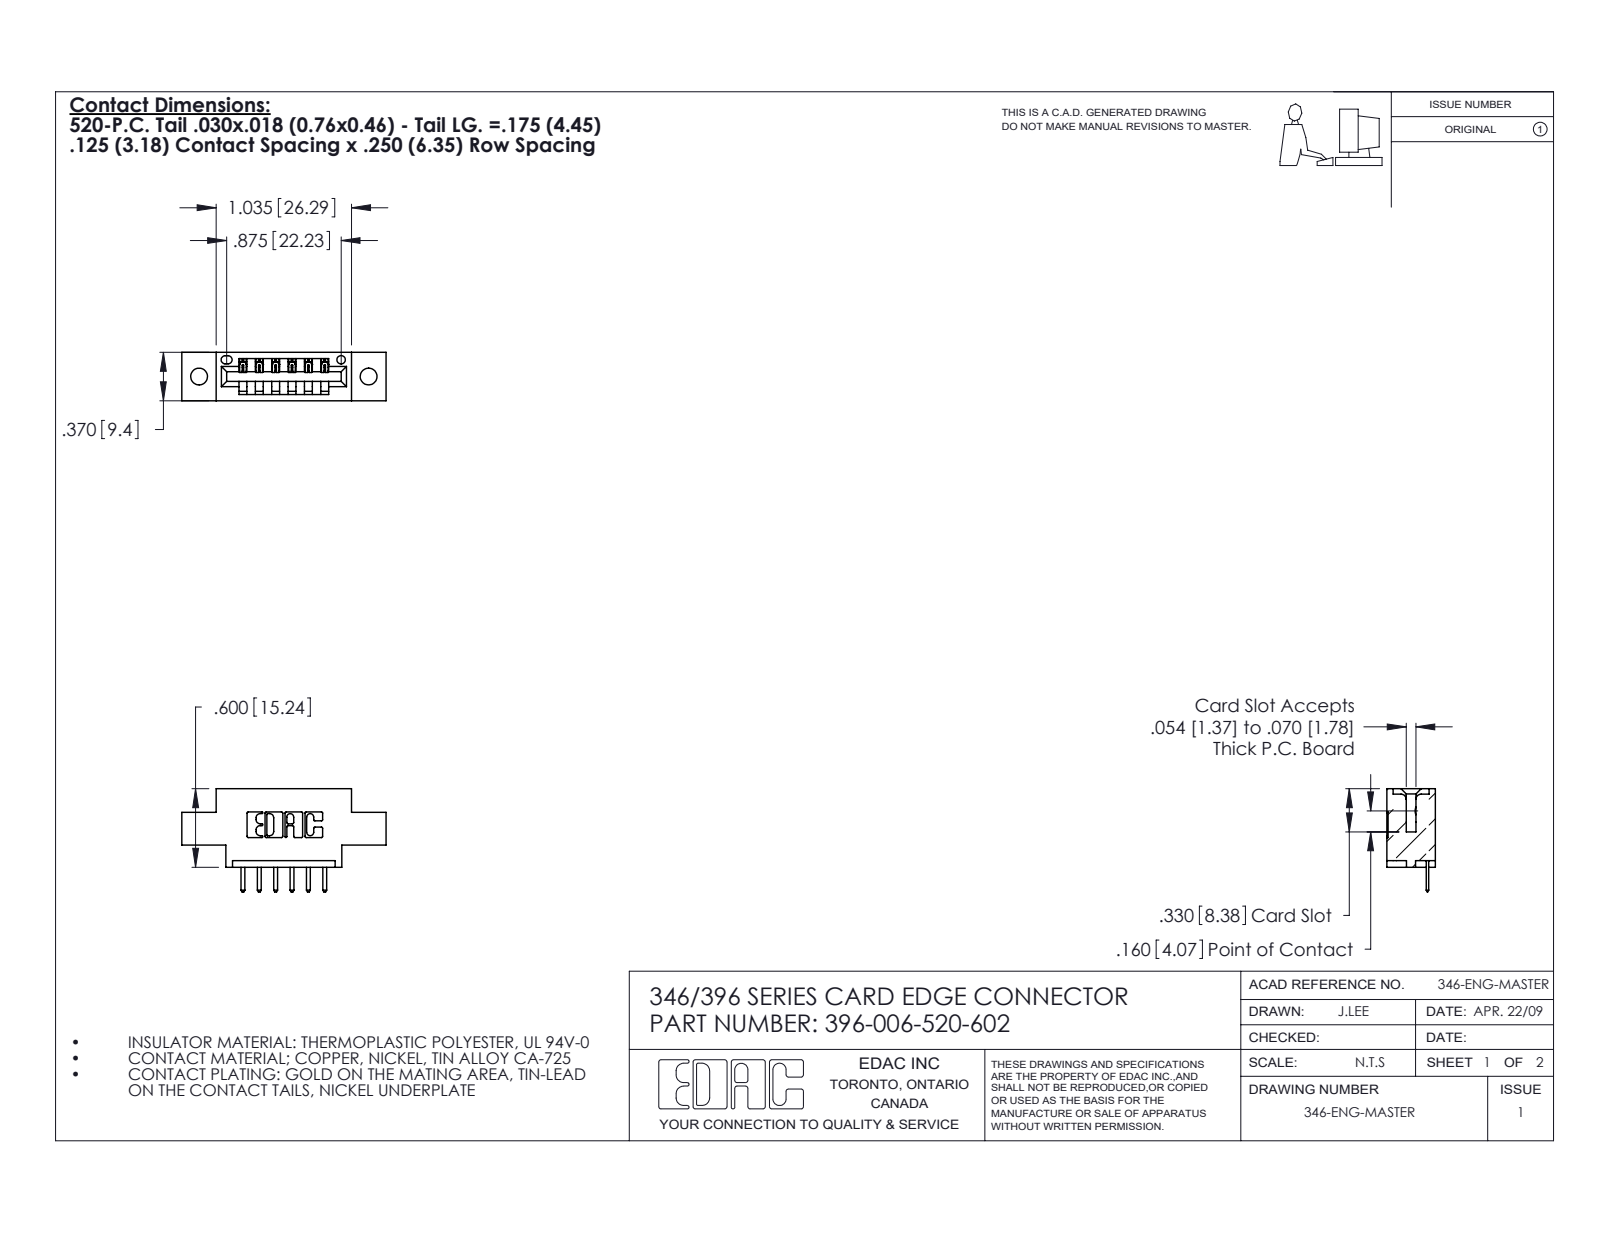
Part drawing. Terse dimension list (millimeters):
name: 345-292-001_345-293-120; 346 Part_0.170 Offset - 0.128 Dia; 396-006-520-602
written by: SolidWorks 2020 (CONFIG_CONTROL_DESIGN)
unit: mm
bodies: 7 solids, 498 faces (332 planar, 166 cylindrical, 0 other)
size: 39.6 × 20 × 9.4
volume: 3 340 mm³; area: 3 613 mm²
holes: 2× ⌀3.3, 1× ⌀1.6
rounds: 22× R0.3, 14× R0.3, 12× R0.2, 6× R0.2, 6× R0.8, 3× R0.7, 2× R0.8, 2× R1
face distances: 6.4, 9.4, 1.2, 8.2, 3.8, 5.6, 2.5, 4.4, 3.2, 4.7
hole spacings: 6.2, 27.7, 32.9
